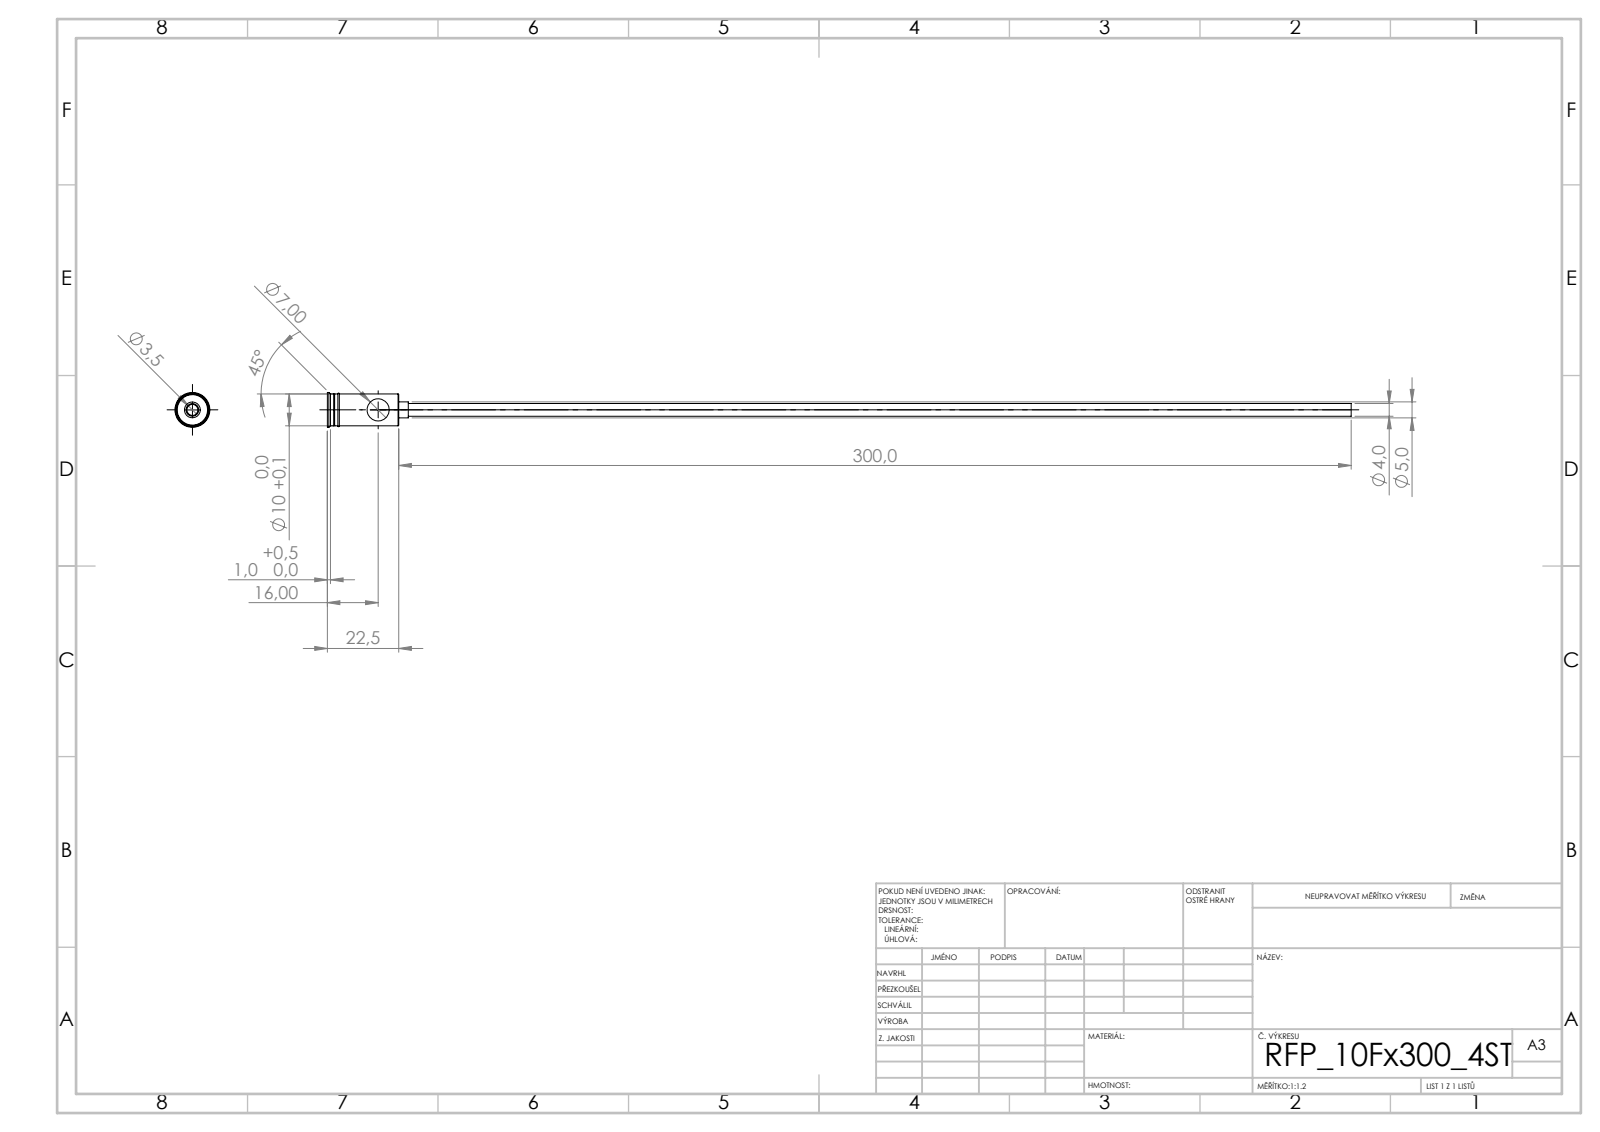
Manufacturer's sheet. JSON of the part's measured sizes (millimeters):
{"step_written_by": "SolidWorks 2019 (CONFIG_CONTROL_DESIGN)", "units": "millimeters", "bodies": {"solids": 1, "faces": 44, "planar": 20, "cylindrical": 16, "other": 8}, "overall_size": [322.5, 11, 11], "volume_mm3": 2246, "surface_area_mm2": 8148, "round_holes": [[3.5, 1], [7, 1]], "round_bosses_or_shafts": [[11, 1], [10, 1], [5, 1], [4, 1]], "face_to_face_distances": [22.5, 20.5, 2, 5.4, 20.2, 2.3, 3, 23.2, 23.5, 25.5]}
